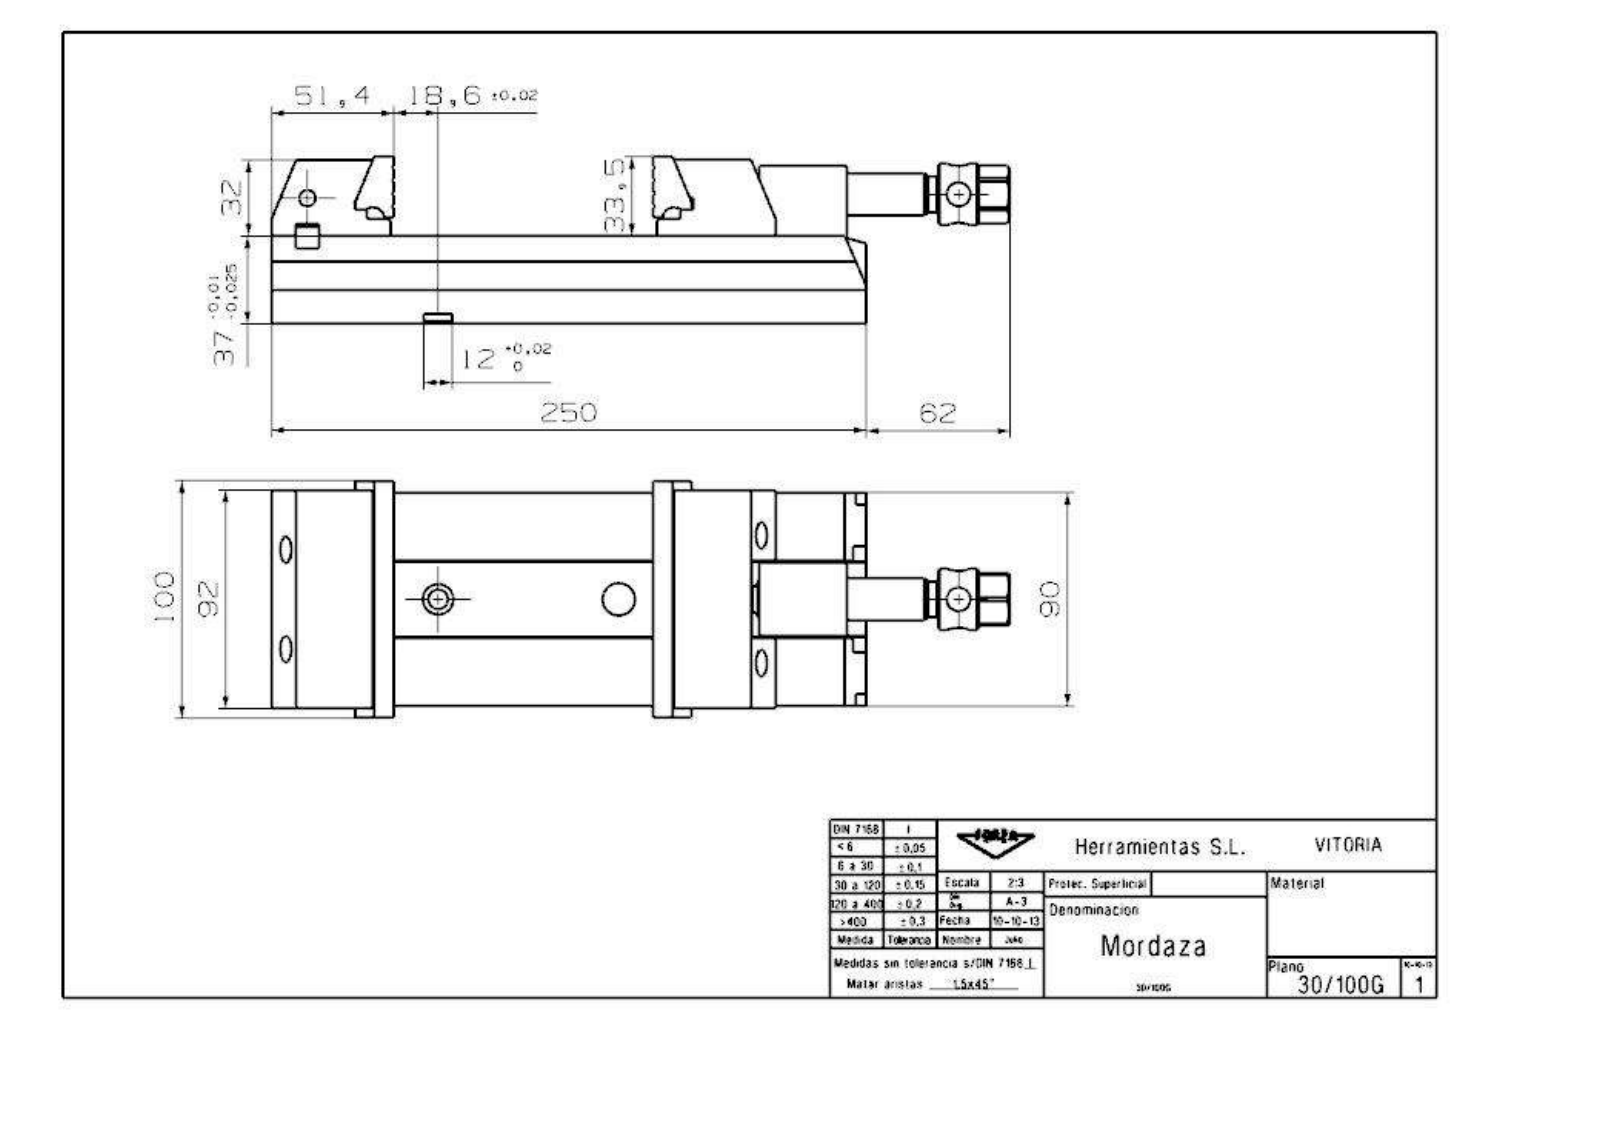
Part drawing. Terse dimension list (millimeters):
name: 30_100G_Mordaza
written by: SIEMENS PLM Software NX 7.5 (AUTOMOTIVE_DESIGN)
unit: mm
bodies: 11 solids, 411 faces (263 planar, 111 cylindrical, 37 other)
size: 310.46 × 100 × 70.5
volume: 897 689 mm³; area: 194 256 mm²
holes: 5× ⌀4.35, 5× ⌀6.99, 5× ⌀13, 4× ⌀5.19, 4× ⌀6.5, 4× ⌀7.5, 4× ⌀11.5, 2× ⌀8.4, 2× ⌀8.5, 2× ⌀10, 2× ⌀10.58, 2× ⌀13.5
bosses: 1× ⌀26, 1× ⌀17.73, 1× ⌀15, 1× ⌀14.5, 1× ⌀10.5
rounds: 16× R0.4, 5× R6, 4× R7.5, 2× R1.2, 2× R5, 2× R5.5, 2× R16.25, 1× R2.5
face distances: 37, 40, 12.3, 5, 90, 35.9, 13.4, 23.6, 22.5, 67.5
hole spacings: 48, 6, 6.01, 42, 54, 11.07, 11.1, 14.17
